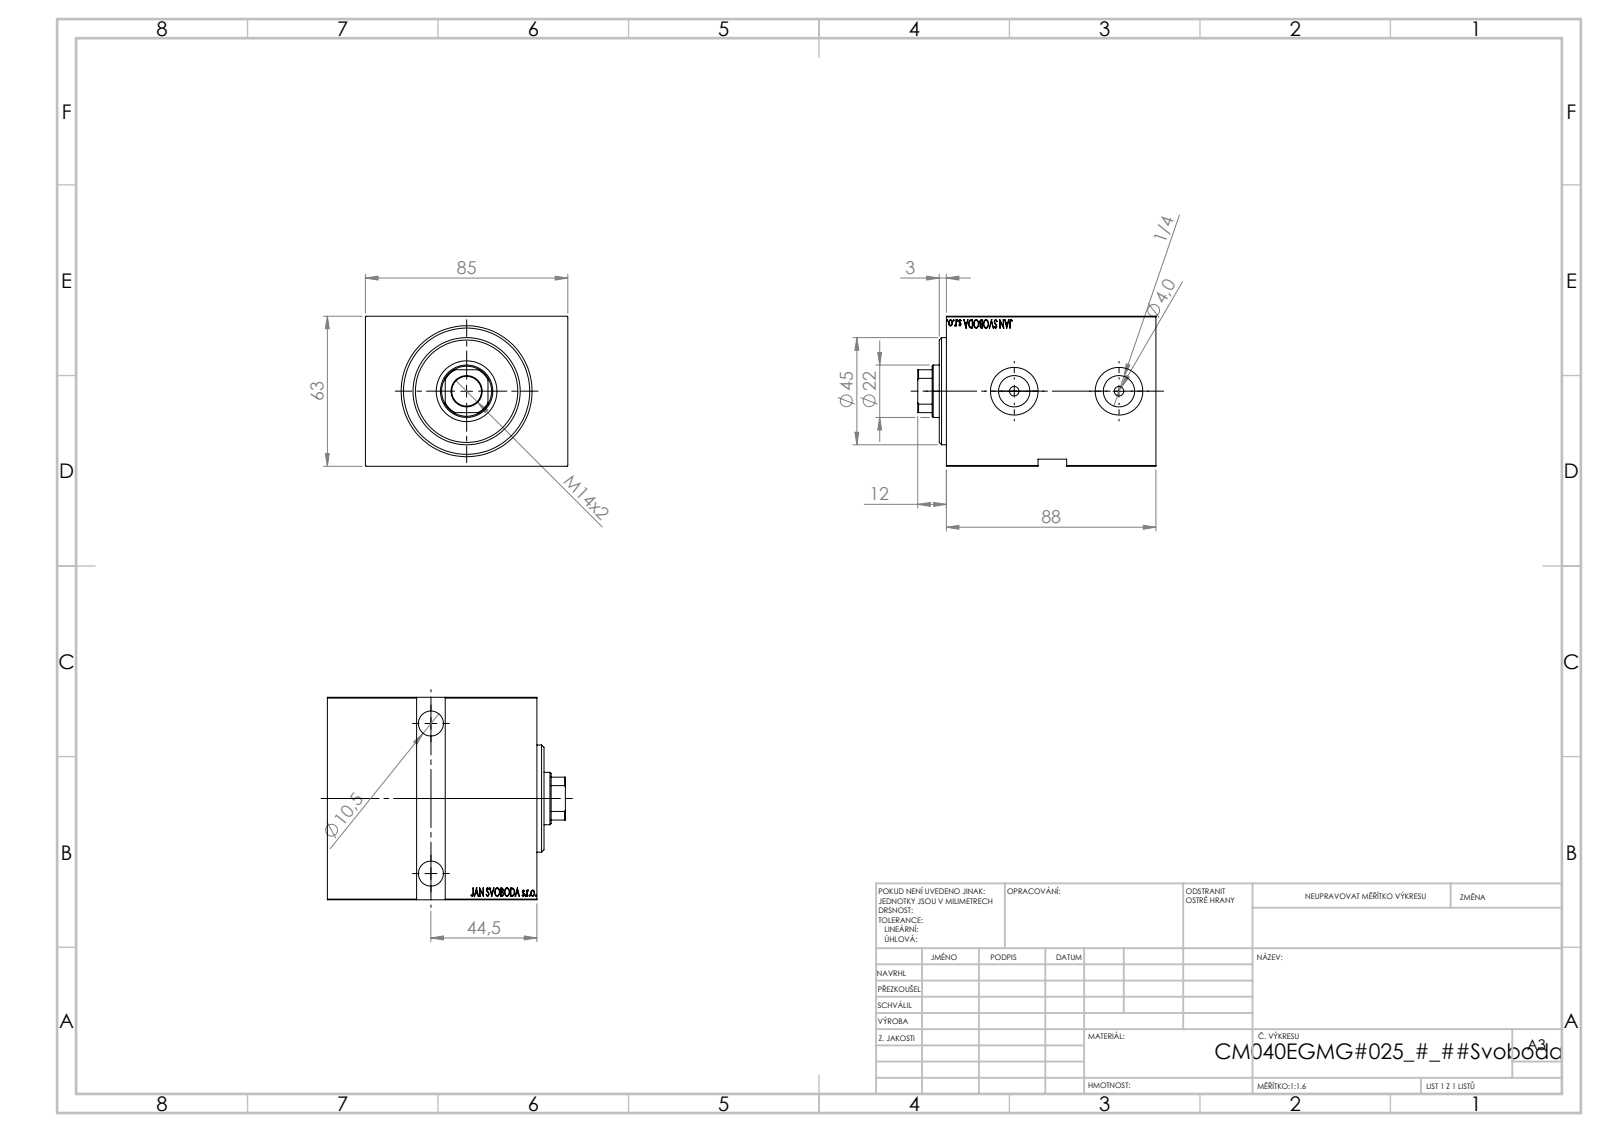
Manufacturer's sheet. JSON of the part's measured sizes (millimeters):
{"part_name": "V450CM_VC_B; V450CM_E_VCP; V450CM_E_Body", "step_written_by": "SolidWorks 2019 (CONFIG_CONTROL_DESIGN)", "units": "millimeters", "bodies": {"solids": 3, "faces": 848, "planar": 410, "cylindrical": 44, "other": 394}, "overall_size": [100, 85, 63], "volume_mm3": 438155, "surface_area_mm2": 71701, "round_holes": [[4, 2], [10.5, 2], [13.16, 2], [16.5, 2], [20, 2], [12.5, 1], [22, 1], [25.5, 1], [40, 1], [53, 1]], "round_bosses_or_shafts": [[45, 1], [42, 1]], "partial_cylinders_radius": [[10.5, 1]], "face_to_face_distances": [63, 85, 88, 12, 76, 3, 5, 83, 71, 40], "hole_center_spacings": [44, 63]}
